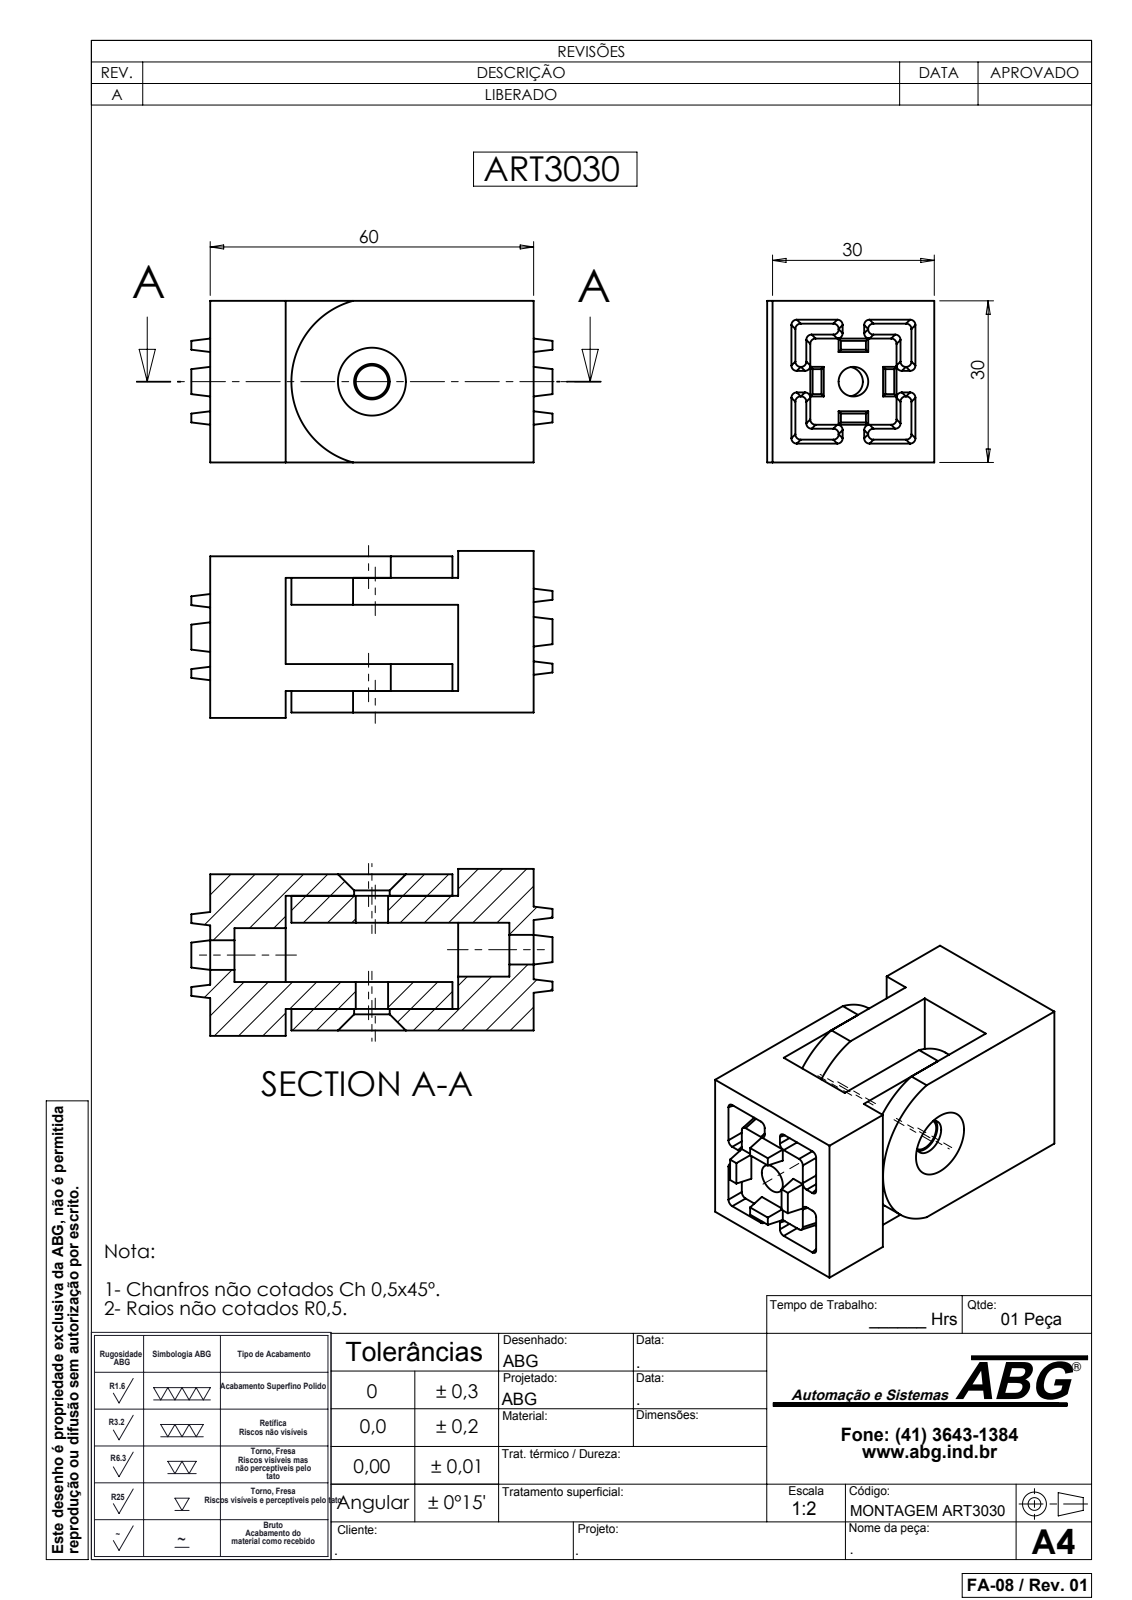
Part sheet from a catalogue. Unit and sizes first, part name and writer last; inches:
Units: inches
Overall size (bounding box): 1.907 × 1.181 × 1.181
Round holes (diameter × count): ⌀0.177 ×1, ⌀0.256 ×1, ⌀0.394 ×1
Partial cylindrical surfaces — rounded edges, fillets, slot ends (radius × count): R0.039 ×24, R0.612 ×1
Main face-to-face distances: 0.197, 1.181, 0.157, 0.787, 0.63, 0.984, 0.827, 0.551, 0.394, 1.024
Volume: 1.103 in³ · Surface area: 13.25 in²
Bodies: 1 solid, 109 faces (60 planar, 42 cylindrical, 7 other)
Part name (STEP PRODUCT): ART3030
STEP written by: SolidWorks 2007 (CONFIG_CONTROL_DESIGN)
